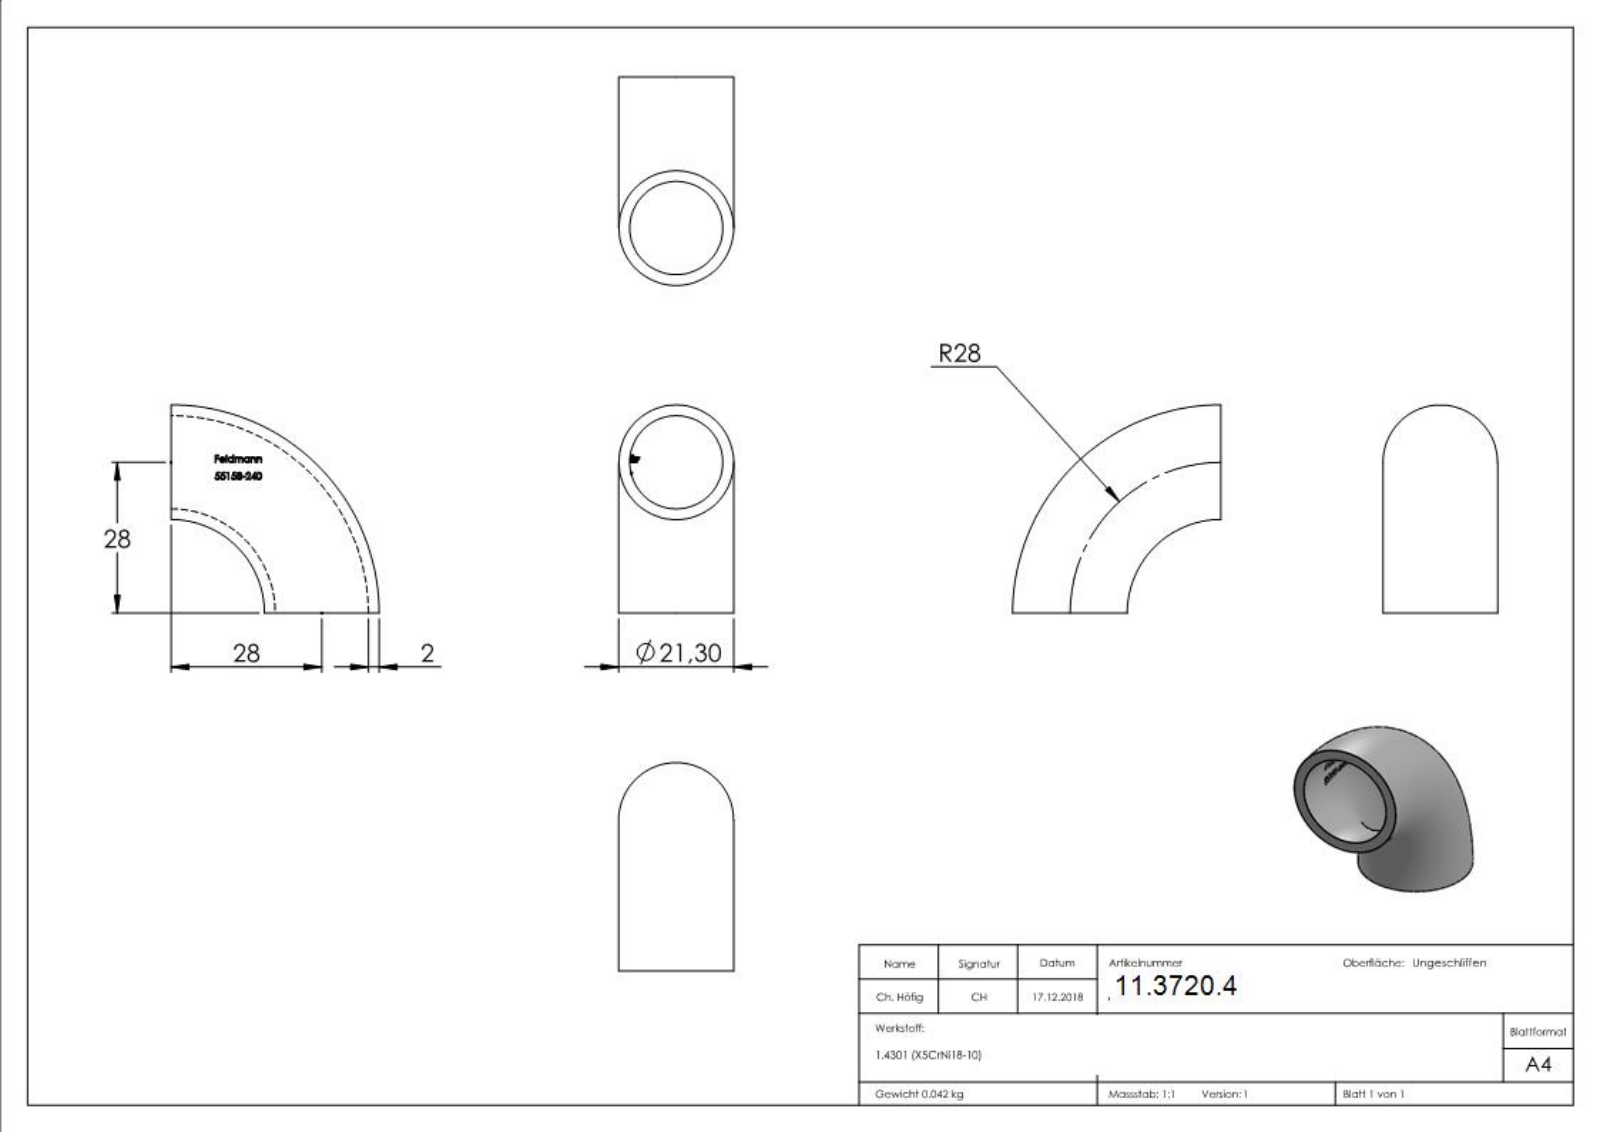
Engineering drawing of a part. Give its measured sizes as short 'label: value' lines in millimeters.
name: 55158-240
written by: SolidWorks 2015 (CONFIG_CONTROL_DESIGN)
unit: mm
bodies: 1 solid, 235 faces (103 planar, 0 cylindrical, 132 other)
size: 38.65 × 38.65 × 21.3
volume: 5 333 mm³; area: 5 586 mm²
face distances: 0.39, 1.12, 1.26, 4.23, 2.02, 4.09, 2.97, 3.66, 3.27, 5.35
